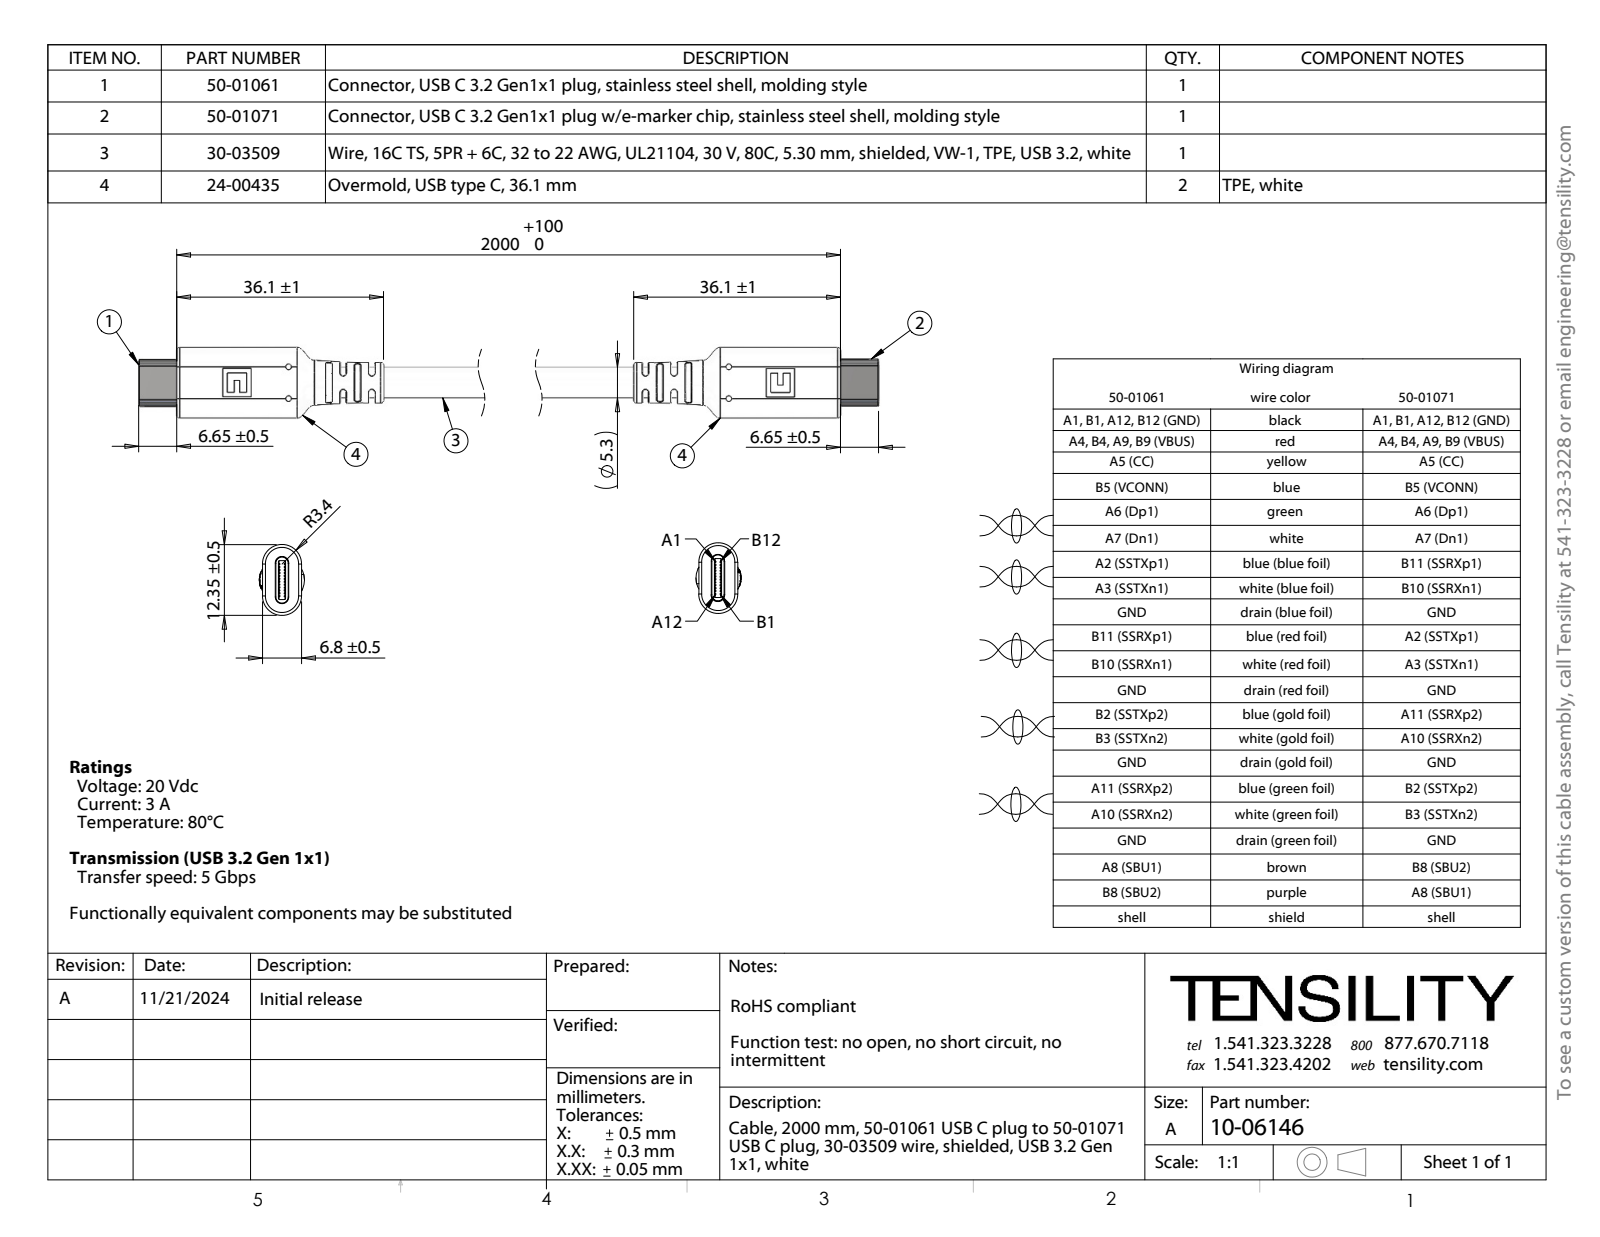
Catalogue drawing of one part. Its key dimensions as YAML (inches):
part_name: "30-03509; 24-00435; 50-01071_Hidden emarker; 50-01061_Hidden emarker (+1 more)"
step_written_by: "SolidWorks 2021 (CONFIG_CONTROL_DESIGN)"
units: inches
bodies: {solids: 168, faces: 1726, planar: 728, cylindrical: 766, other: 232}
overall_size: [8.48, 0.486, 0.311]
volume: 0.413
surface_area: 76.59
round_holes:
  - {diameter: 0.039, count: 4}
  - {diameter: 0.164, count: 1}
  - {diameter: 0.164, count: 1}
  - {diameter: 0.165, count: 1}
  - {diameter: 0.165, count: 1}
  - {diameter: 0.173, count: 1}
round_bosses_or_shafts:
  - {diameter: 0.029, count: 8}
  - {diameter: 0.019, count: 4}
  - {diameter: 0.01, count: 4}
  - {diameter: 0.022, count: 2}
  - {diameter: 0.308, count: 1}
  - {diameter: 0.209, count: 1}
  - {diameter: 0.039, count: 1}
  - {diameter: 0.035, count: 1}
partial_cylinders:
  - {radius: 0.02, count: 20}
  - {radius: 0.01, count: 8}
  - {radius: 0.004, count: 4}
  - {radius: 0.006, count: 4}
  - {radius: 0.046, count: 4}
  - {radius: 0.012, count: 2}
  - {radius: 0.012, count: 2}
  - {radius: 0.019, count: 2}
face_to_face_distances: [0.041, 0.038, 0.041, 0.04, 0.043, 0.268, 0.024, 0.098, 0.038, 0.039]
hole_center_spacings: [0.083, 0.025, 0.098, 0.082, 0.085, 0.023, 0.024, 0.081]
